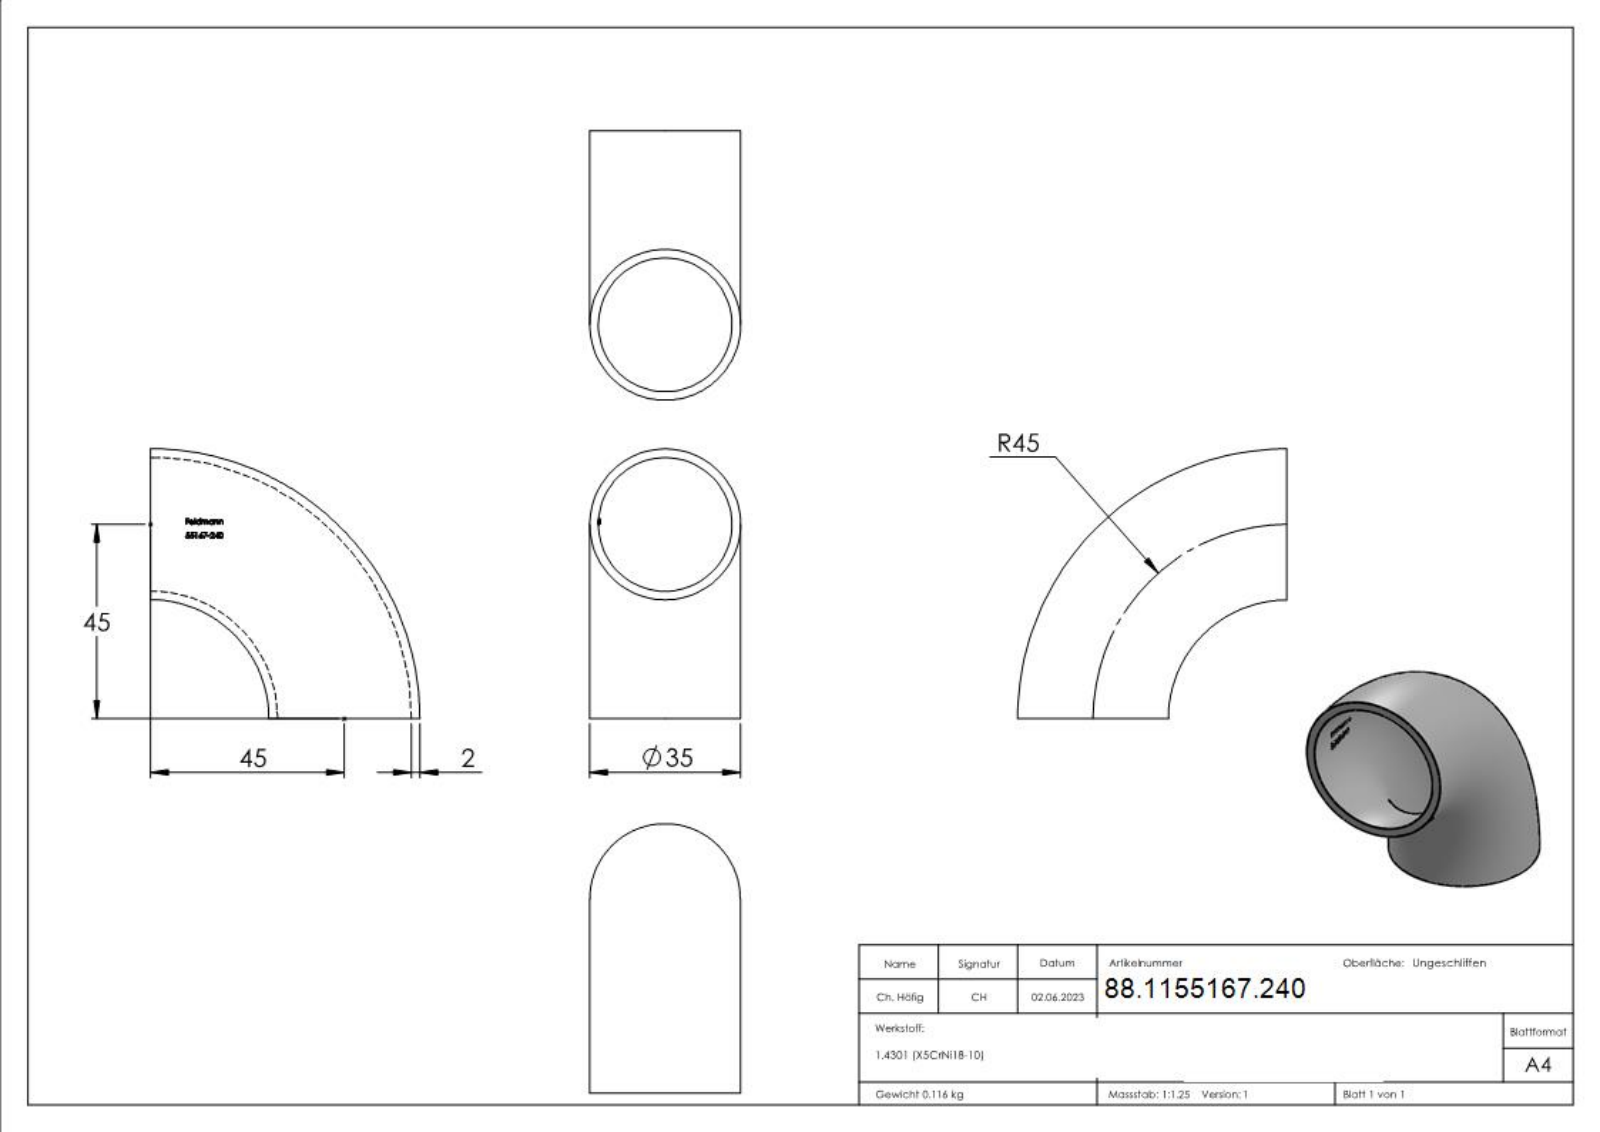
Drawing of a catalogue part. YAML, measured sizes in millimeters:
part_name: "55167-240"
step_written_by: "SolidWorks 2018 (CONFIG_CONTROL_DESIGN)"
units: millimeters
bodies: {solids: 1, faces: 219, planar: 106, cylindrical: 0, other: 113}
overall_size: [62.5, 62.5, 35]
volume: 14656
surface_area: 15080
face_to_face_distances: [0.39, 1.26, 2.97, 1.32, 4.23, 2.02, 0.99, 0.87, 3.66, 3.27]
